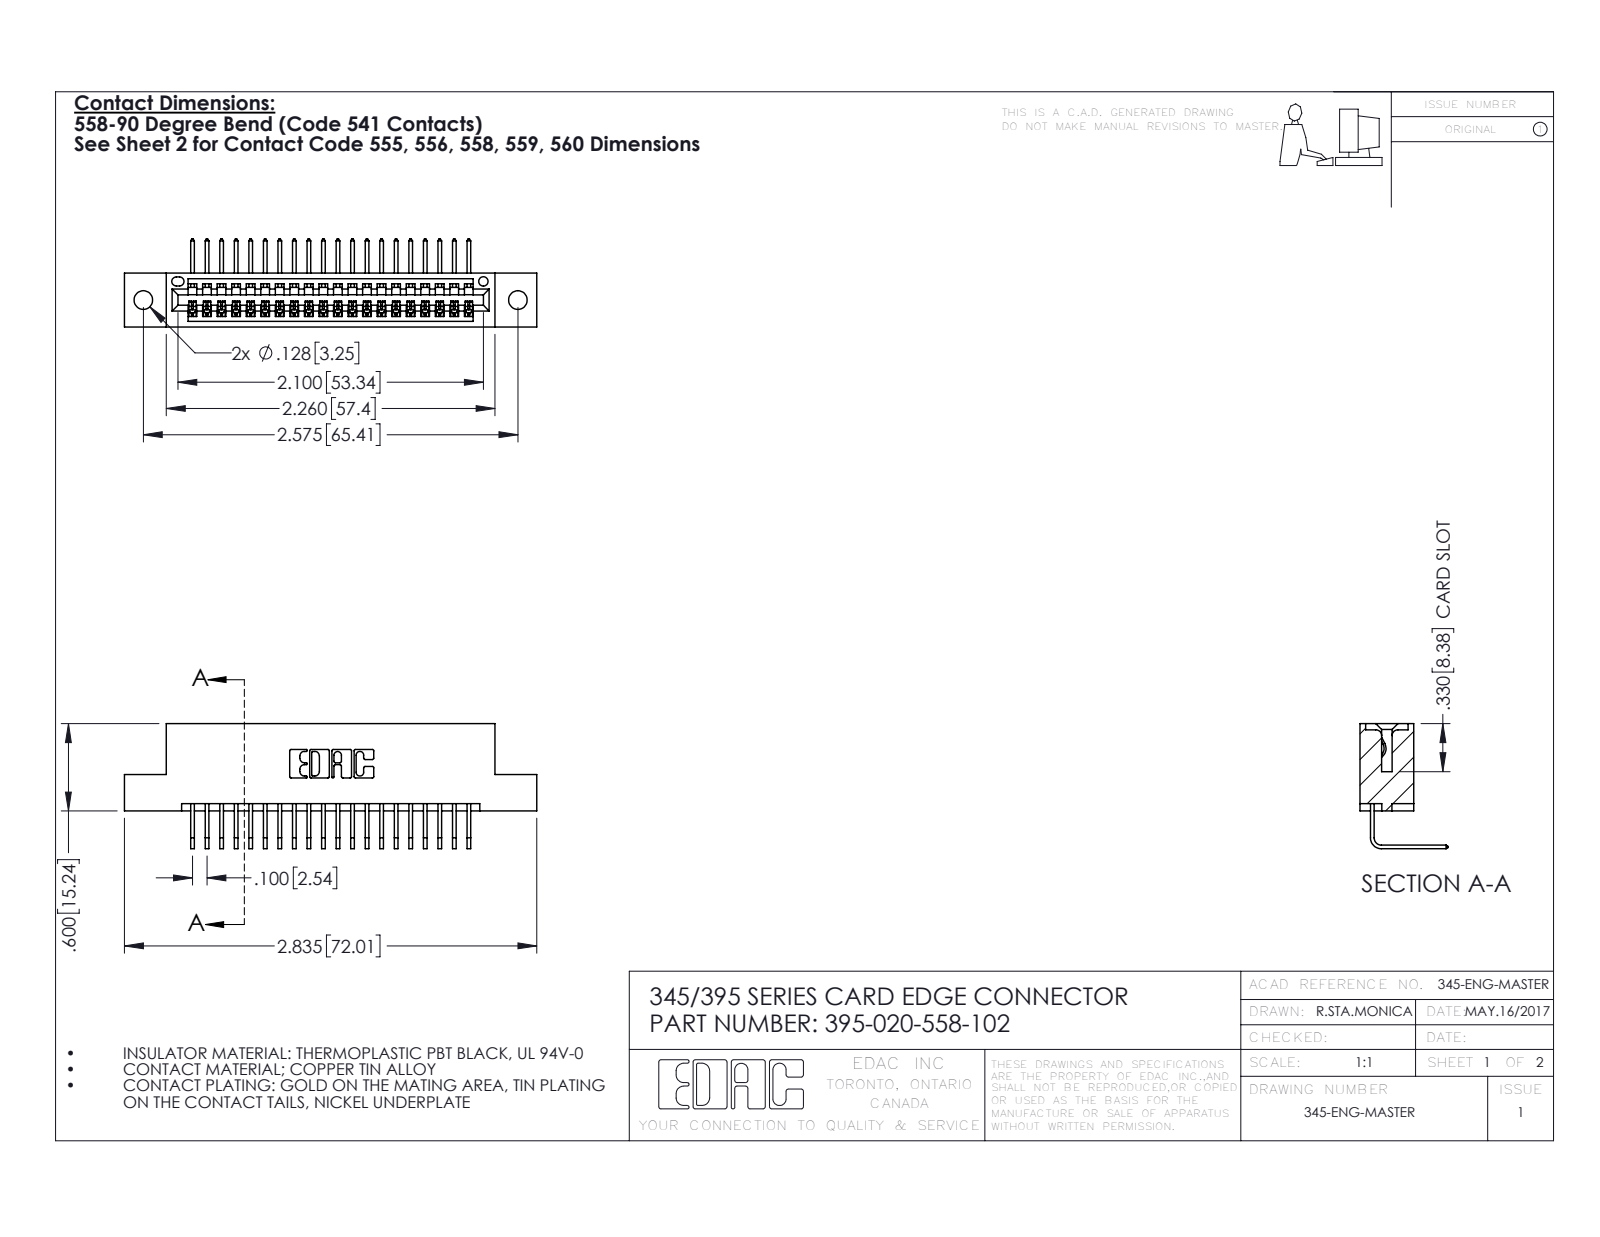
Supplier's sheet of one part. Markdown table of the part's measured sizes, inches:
| quantity | value |
| --- | --- |
| part name | 345 Part_Flush Mounting Lugs - 0.128 Dia; 345-292-001_558 Tail - 2; 395-020-558-102 |
| STEP written by | SolidWorks 2016 (CONFIG_CONTROL_DESIGN) |
| units | inches |
| bodies | 21 solids, 1326 faces (920 planar, 406 cylindrical, 0 other) |
| overall size | 2.835 × 0.859 × 0.605 |
| volume | 0.408 in³ |
| surface area | 13.5 in² |
| round holes (diameter × count) | 0.128 × 2, 0.064 × 1 |
| partial cylindrical surfaces (radius × count) | 0.006 × 40, 0.01 × 22, 0.007 × 6, 0.031 × 6, 0.026 × 3, 0.031 × 2, 0.04 × 2, 0.014 × 1 |
| main face-to-face distances | 0.298, 0.072, 0.2, 0.37, 0.098, 0.272, 0.025, 0.225, 0.149, 0.6 |
| hole center spacings | 0.27, 2.341, 2.575 |
